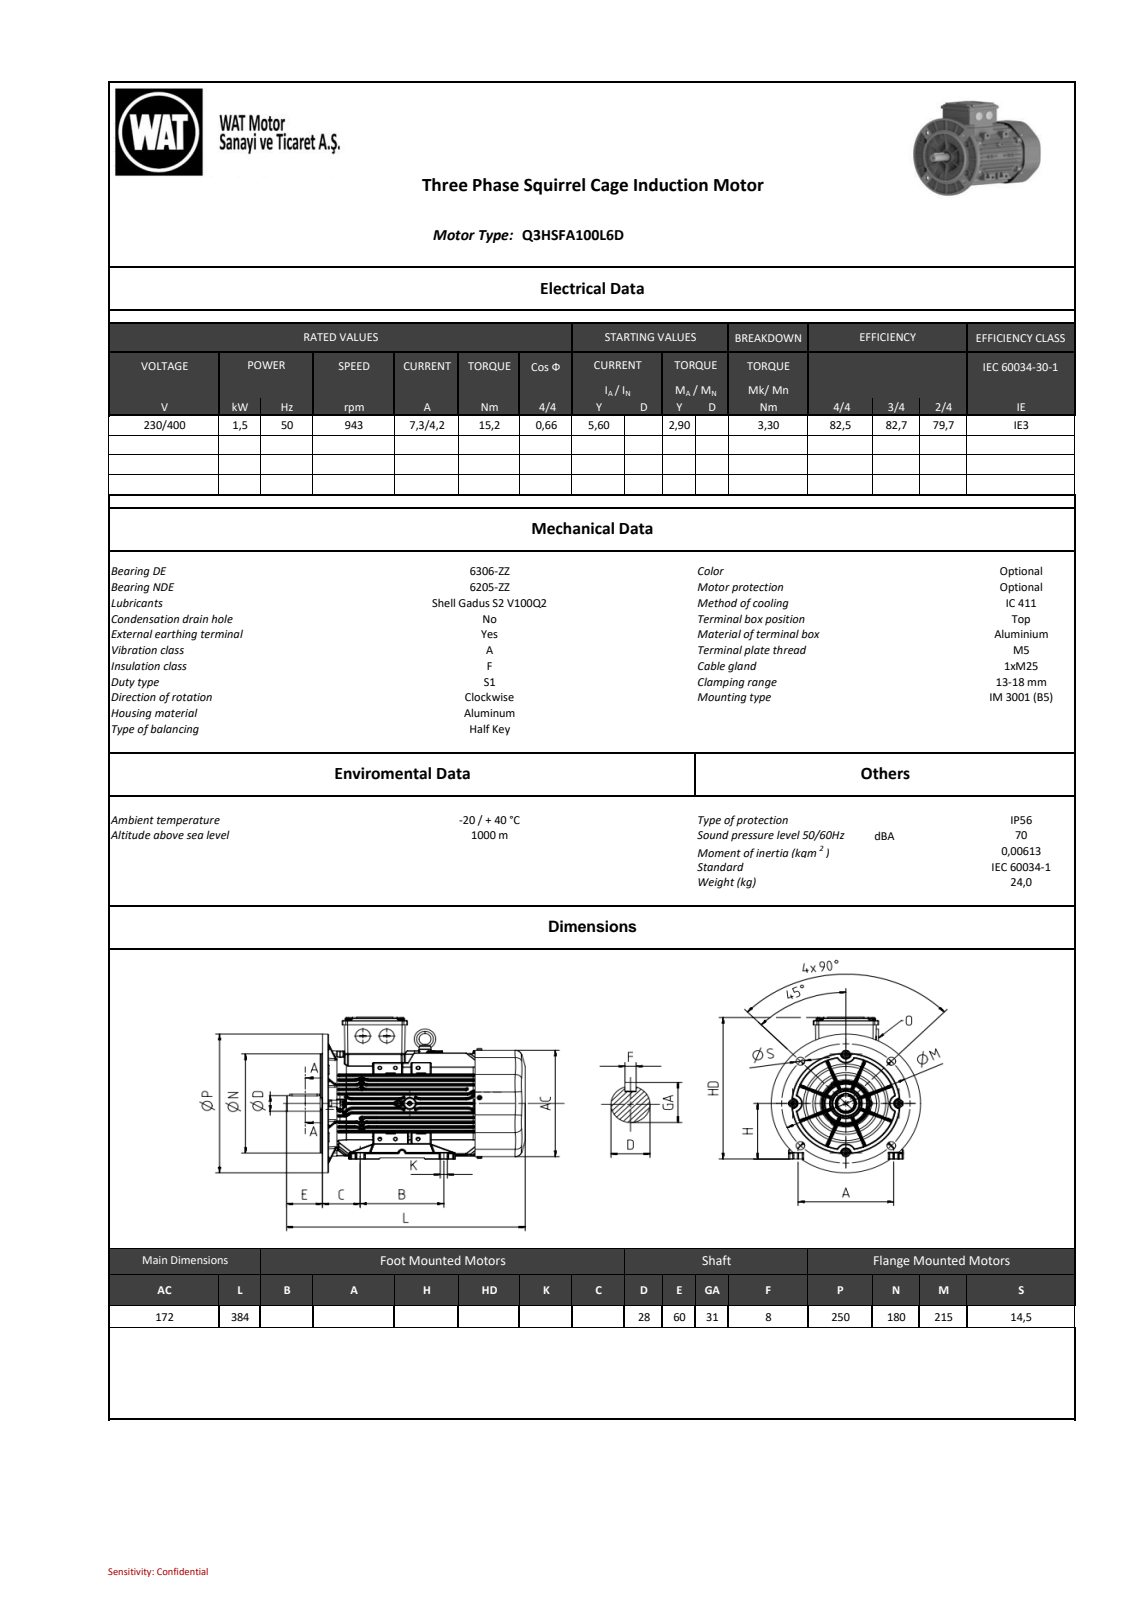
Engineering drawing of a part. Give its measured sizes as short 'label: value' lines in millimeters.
name: QHS Series_ 100_B5 DEEP COVER_stp_objects
written by: SIEMENS PLM Software NX2206.8101 (AUTOMOTIVE_DESIGN)
unit: mm
bodies: 0 solids, 6516 faces (1592 planar, 2742 cylindrical, 2182 other)
size: 384.19 × 258.21 × 250.32
holes: 4× ⌀11, 1× ⌀8.5, 1× ⌀9.87, 1× ⌀10.5, 1× ⌀79.79, 1× ⌀97.79, 1× ⌀115.78
bosses: 7× ⌀8, 6× ⌀5, 4× ⌀10, 2× ⌀25, 1× ⌀180, 1× ⌀102.19, 1× ⌀84.19, 1× ⌀30
rounds: 835× R1, 689× R0.8, 231× R0.5, 69× R2, 28× R8, 11× R1.5, 10× R4, 8× R0.8
face distances: 7.5, 222, 91.91, 8.93, 82.98, 23.57, 4, 50.35, 16, 206
hole spacings: 79.4, 112.29, 158.8, 79.25, 79.55
